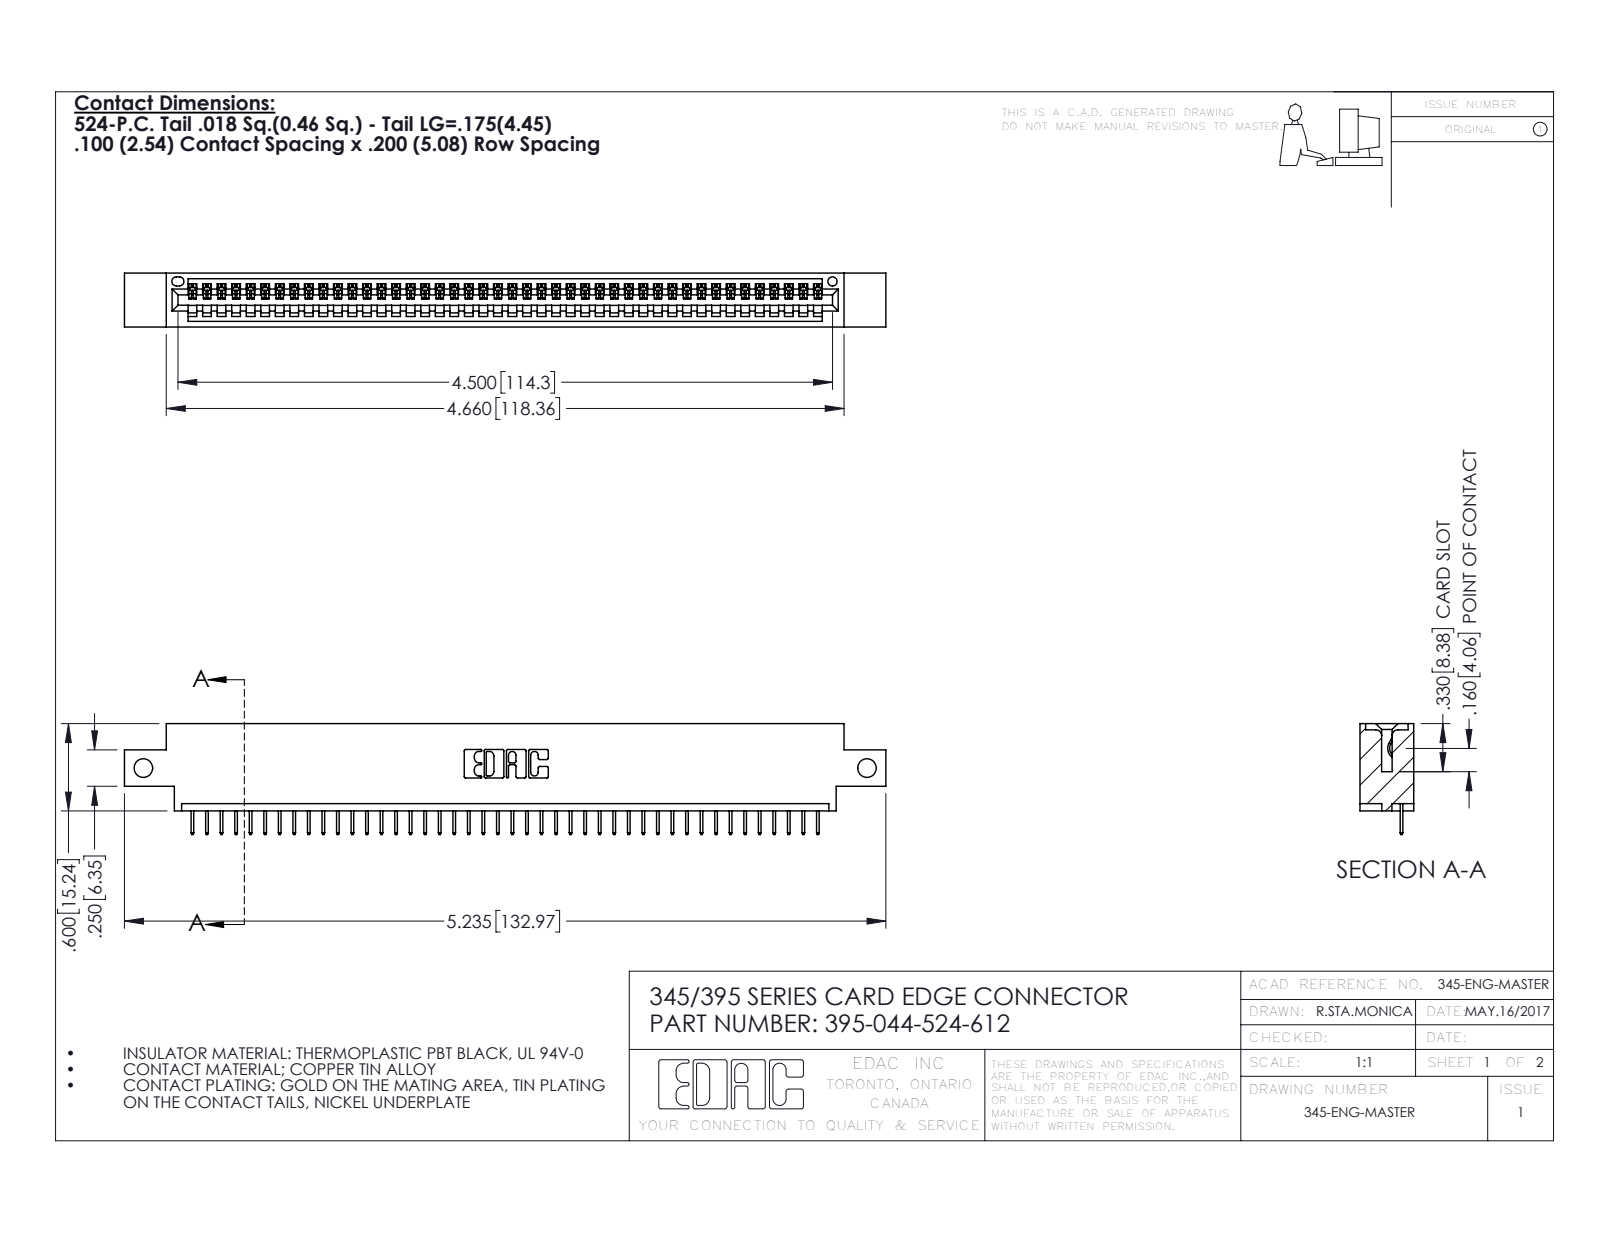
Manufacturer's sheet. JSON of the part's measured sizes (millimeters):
{"part_name": "395-044-524-612; 345 Part_0.170 Offset - Side Mount; 345-292-001_345-293-124", "step_written_by": "SolidWorks 2016 (CONFIG_CONTROL_DESIGN)", "units": "millimeters", "bodies": {"solids": 45, "faces": 2858, "planar": 2108, "cylindrical": 750, "other": 0}, "overall_size": [133, 19.4, 9.4], "volume_mm3": 12300, "surface_area_mm2": 15760, "round_holes": [[3.3, 2], [1.6, 1]], "partial_cylinders_radius": [[0.2, 88], [0.3, 22], [0.2, 6], [0.8, 6], [0.7, 3], [0.8, 2], [1, 2], [0.4, 1]], "face_to_face_distances": [1.8, 7.6, 9.4, 5.1, 2.5, 6.9, 0.6, 5.7, 1.8, 4.4], "hole_center_spacings": [126.4]}
